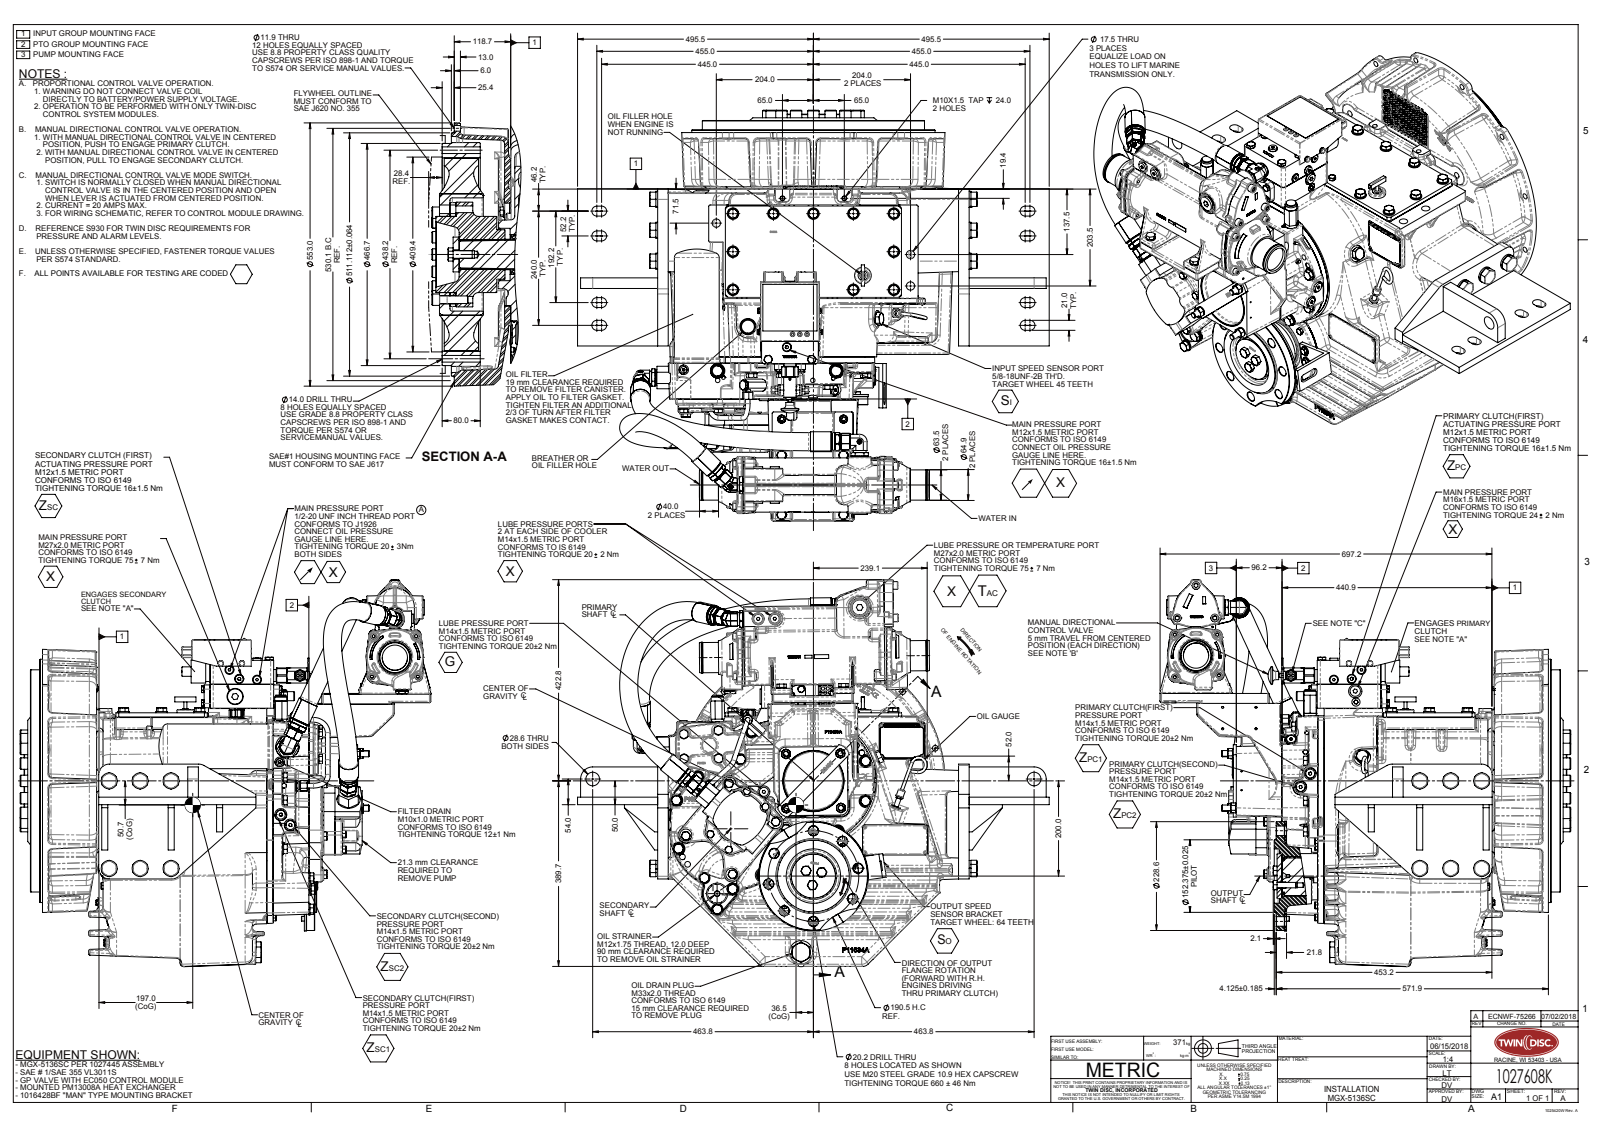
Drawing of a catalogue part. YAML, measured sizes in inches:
part_name: "1027608K"
step_written_by: "SolidWorks 2015 (AUTOMOTIVE_DESIGN)"
units: inches
bodies: {solids: 0, faces: 5906, planar: 1971, cylindrical: 1784, other: 2151}
overall_size: [39.016, 33.973, 32.011]
round_holes:
  - {diameter: 0.276, count: 62}
  - {diameter: 0.469, count: 12}
  - {diameter: 0.795, count: 11}
  - {diameter: 0.551, count: 8}
  - {diameter: 0.394, count: 7}
  - {diameter: 0.984, count: 7}
  - {diameter: 0.165, count: 6}
  - {diameter: 0.346, count: 6}
  - {diameter: 0.266, count: 4}
  - {diameter: 0.367, count: 3}
  - {diameter: 0.472, count: 3}
  - {diameter: 0.689, count: 3}
round_bosses_or_shafts:
  - {diameter: 0.945, count: 40}
  - {diameter: 0.512, count: 8}
  - {diameter: 0.781, count: 7}
  - {diameter: 0.744, count: 7}
  - {diameter: 1.323, count: 6}
  - {diameter: 0.394, count: 6}
  - {diameter: 1.252, count: 5}
  - {diameter: 1.65, count: 4}
partial_cylinders:
  - {radius: 0.118, count: 132}
  - {radius: 0.157, count: 122}
  - {radius: 0.079, count: 70}
  - {radius: 0.098, count: 69}
  - {radius: 0.315, count: 68}
  - {radius: 0.197, count: 46}
  - {radius: 0.256, count: 44}
  - {radius: 0.63, count: 25}
face_to_face_distances: [0.015, 0.875, 24.891, 0.625, 0.515, 0.531, 7.601, 6.976, 0.031, 14.074]
hole_center_spacings: [3.75, 7.048, 2.565, 5.746, 2.565, 4.821, 5.119, 7.5]
